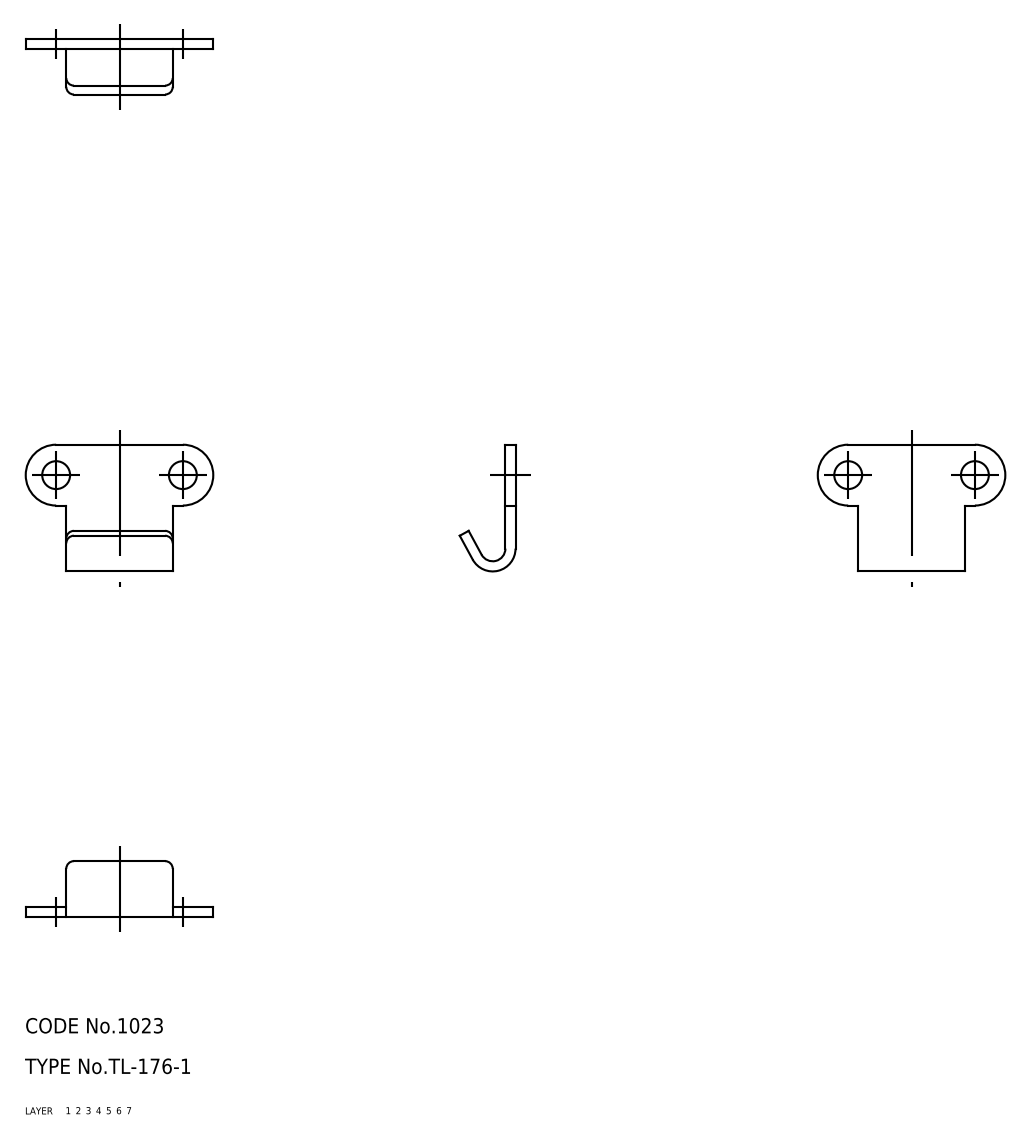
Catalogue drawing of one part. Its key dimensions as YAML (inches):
part_name: "keeper"
step_written_by: "CADfix (AUTOMOTIVE_DESIGN)"
units: inches
bodies: {solids: 1, faces: 20, planar: 0, cylindrical: 0, other: 20}
overall_size: [1.457, 0.984, 0.433]
volume: 0.104
surface_area: 3.151
